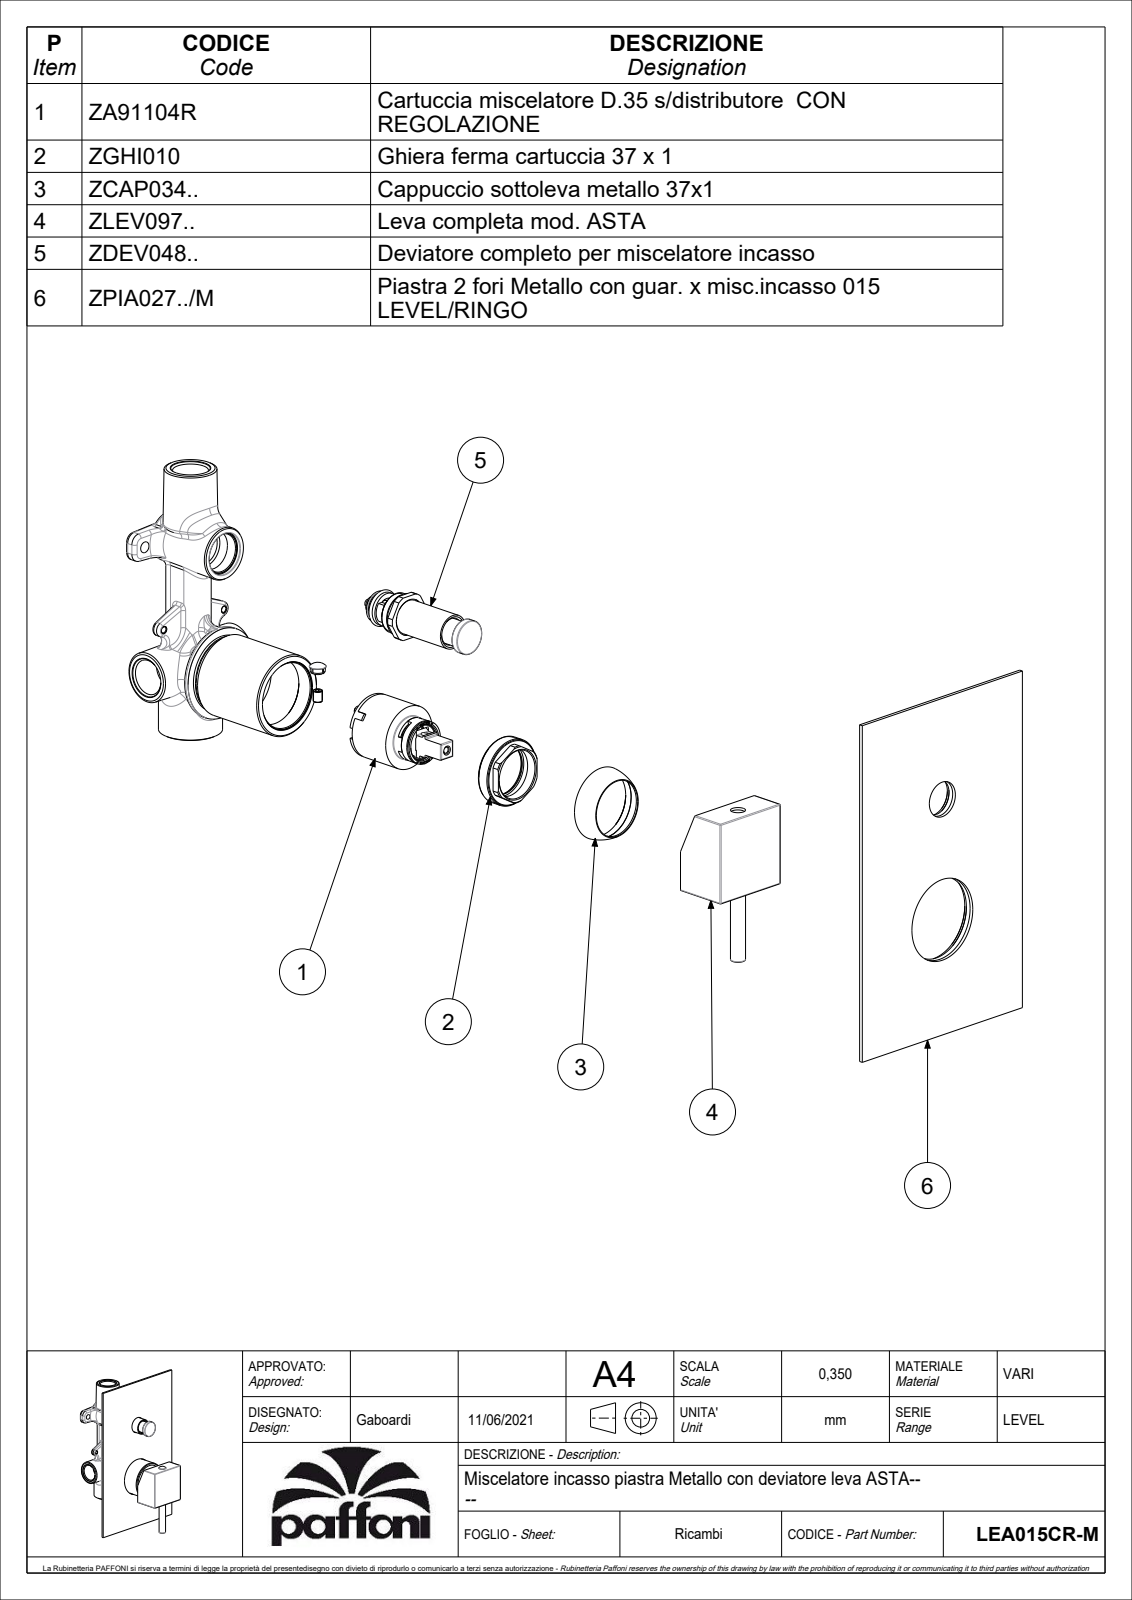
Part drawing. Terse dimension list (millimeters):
name: LEA015CR-M
written by: CREO PARAMETRIC BY PTC INC, 2020044 (CONFIG_CONTROL_DESIGN)
unit: mm
bodies: 5 solids, 905 faces (580 planar, 194 cylindrical, 131 other)
size: 190 × 120 × 55.05
volume: 87 423 mm³; area: 82 732 mm²
holes: 2× ⌀4, 2× ⌀19.5, 1× ⌀3.3, 1× ⌀5, 1× ⌀5.5, 1× ⌀6, 1× ⌀8.1, 1× ⌀10.5, 1× ⌀14.8, 1× ⌀19.9, 1× ⌀26.8, 1× ⌀29
bosses: 1× ⌀44.8, 1× ⌀35, 1× ⌀23.5, 1× ⌀23.4, 1× ⌀21.8, 1× ⌀18.7, 1× ⌀18.6, 1× ⌀14
rounds: 16× R0.5, 11× R0.15, 4× R0.3, 2× R1, 1× R7, 1× R9.3, 1× R10.85, 1× R11.25
face distances: 2, 45, 54.8, 52.8, 3, 51.8, 49.8, 1.5, 27, 4.5
hole spacings: 14.6, 68
